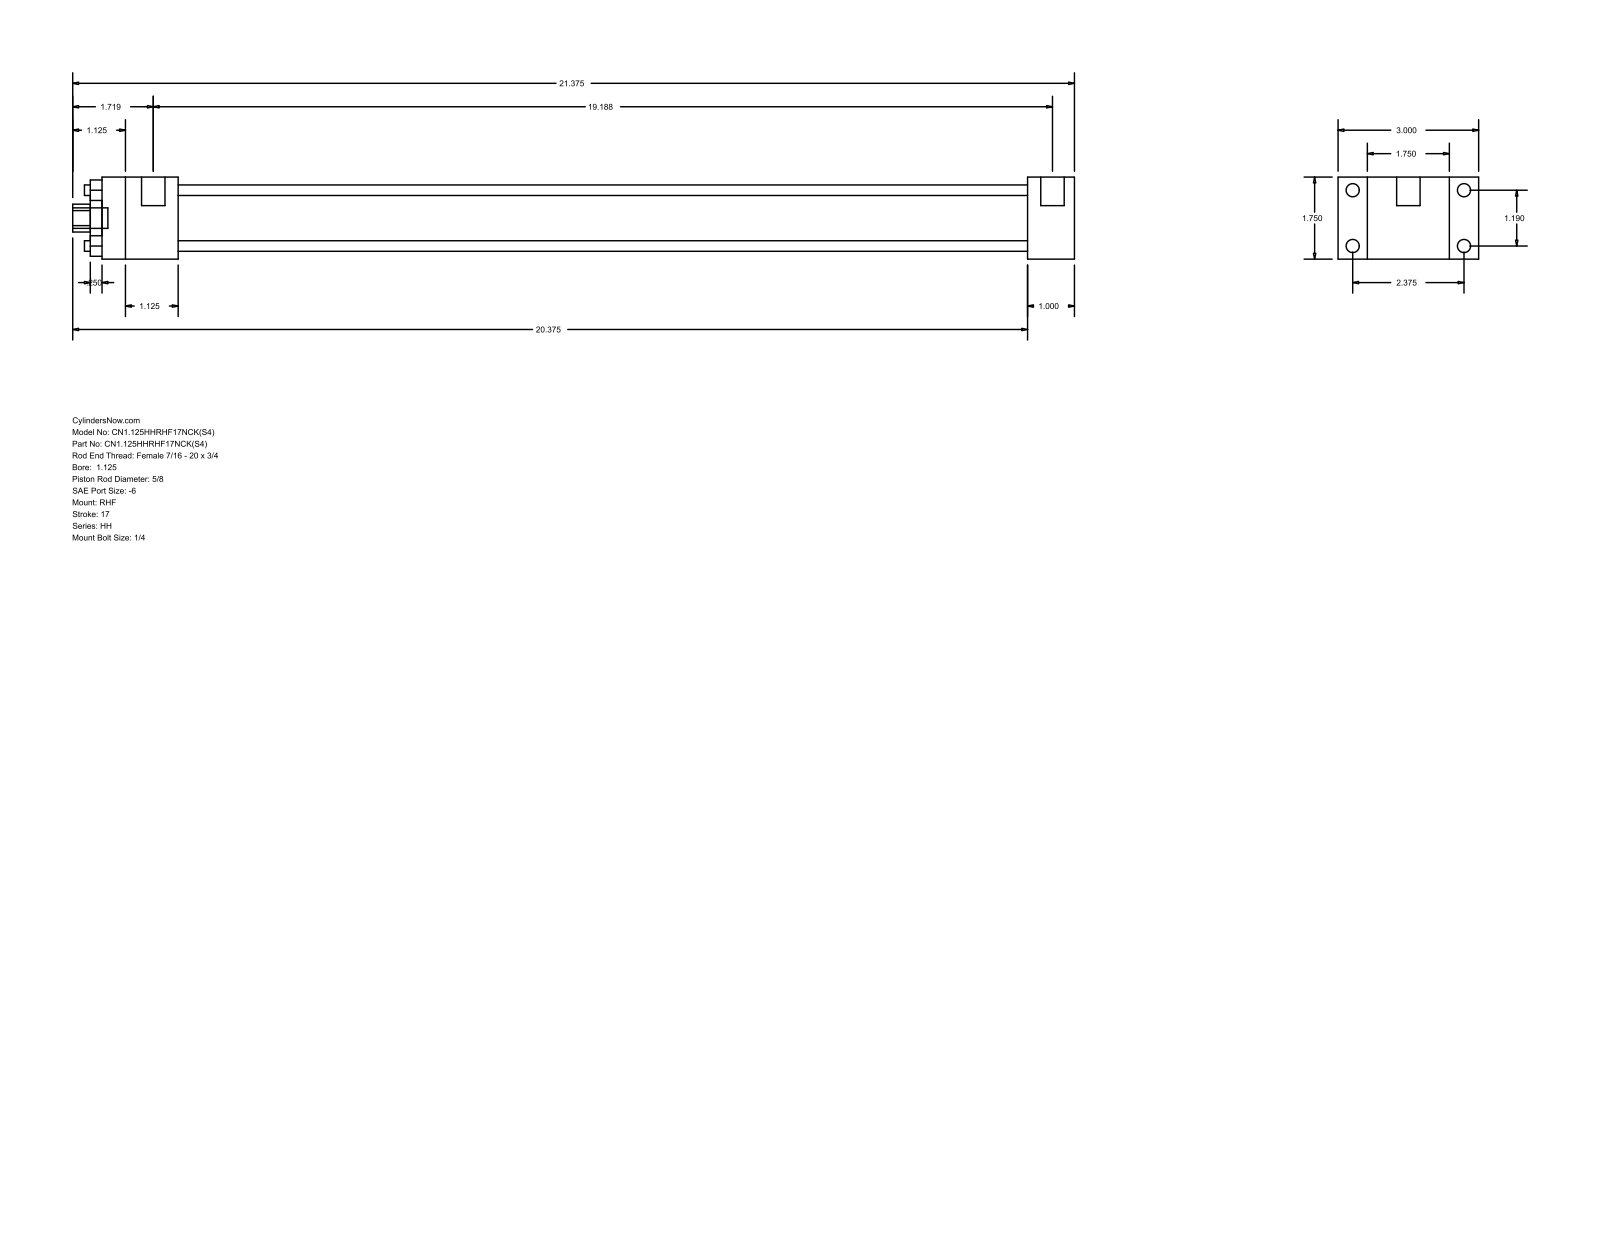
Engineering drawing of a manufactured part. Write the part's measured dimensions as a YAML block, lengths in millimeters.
part_name: "HH_RHF__0112_0.625"
step_written_by: "GSSL Pune (CONFIG_CONTROL_DESIGN)"
units: millimeters
bodies: {solids: 0, faces: 88, planar: 60, cylindrical: 28, other: 0}
overall_size: [542.92, 76.2, 44.45]
round_holes:
  - {diameter: 5.71, count: 4}
  - {diameter: 15.88, count: 1}
  - {diameter: 28.57, count: 1}
  - {diameter: 34.92, count: 1}
round_bosses_or_shafts:
  - {diameter: 7.14, count: 4}
  - {diameter: 5.56, count: 4}
  - {diameter: 12.7, count: 2}
  - {diameter: 11.11, count: 1}
partial_cylinders:
  - {radius: 7.54, count: 1}
face_to_face_distances: [44.46, 15.87, 60.33, 25.4, 76.2, 460.37, 485.77, 41.27, 501.64, 527.04]
hole_center_spacings: [21.37, 30.22, 42.74]
